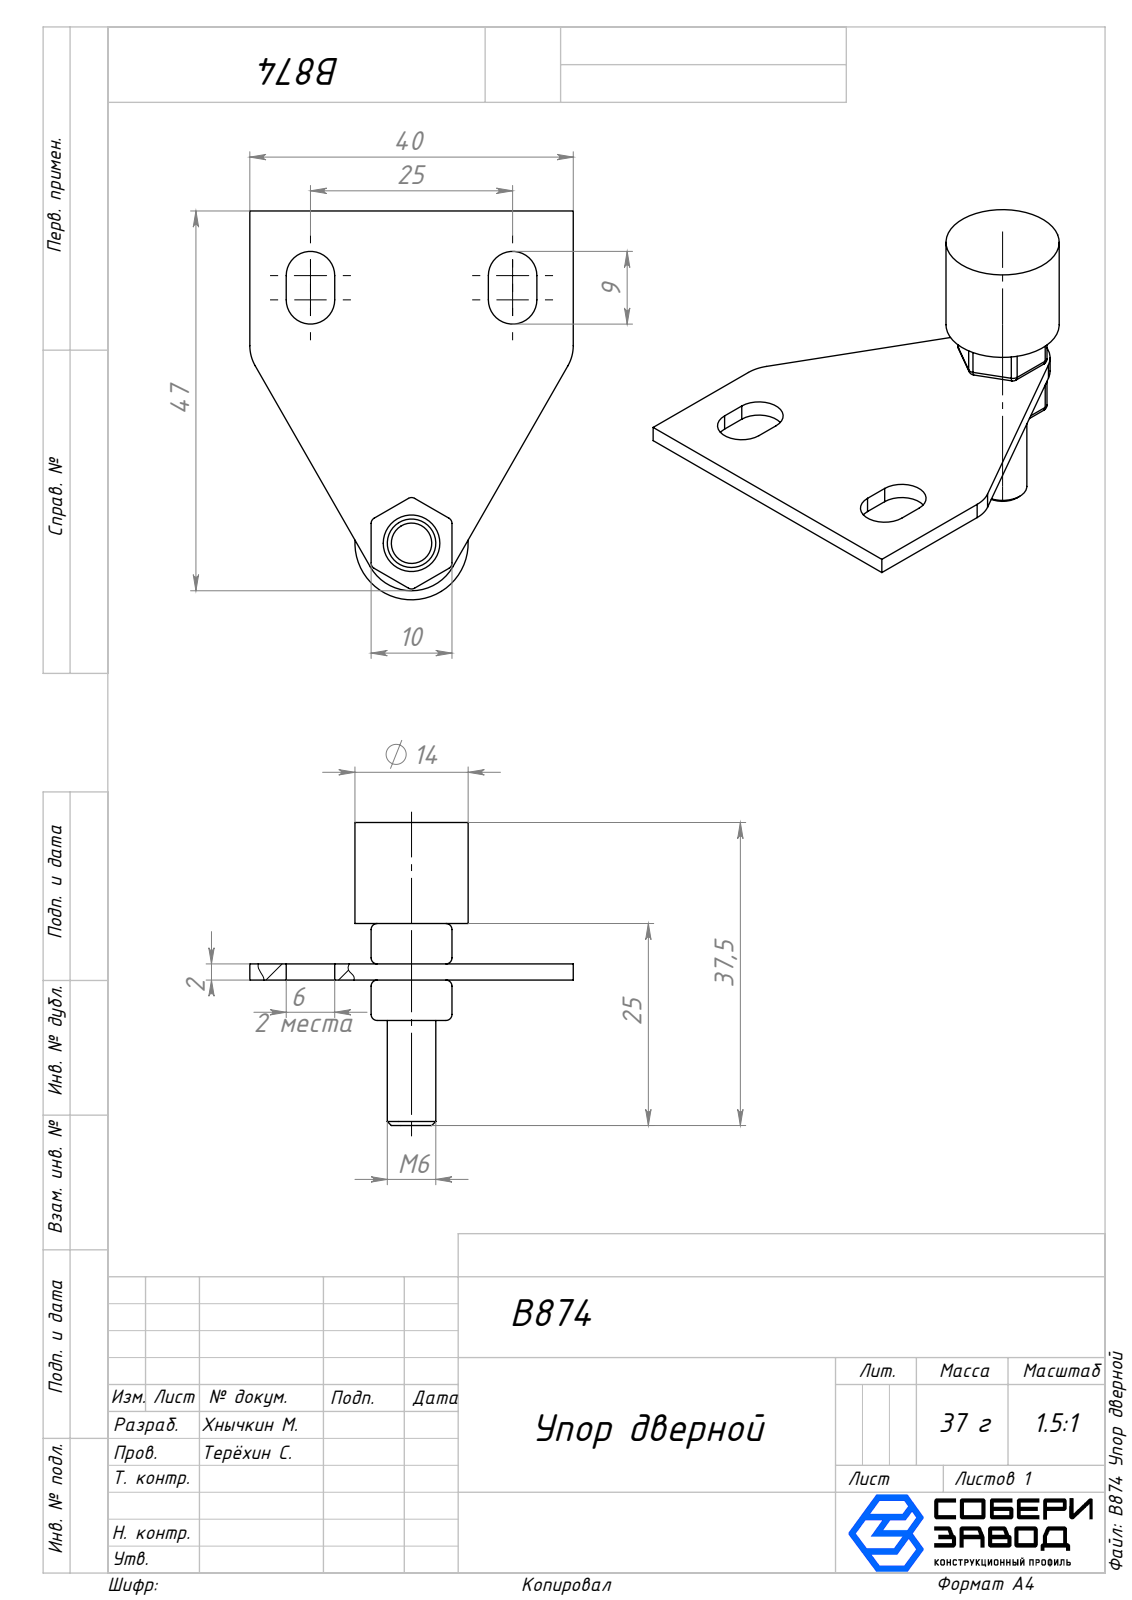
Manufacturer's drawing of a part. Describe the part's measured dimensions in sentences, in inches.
The part is named "Винт_00; B874 Упор дверной; Пластина_00; Гайка_00". Its 3-D file was written by "SolidWorks 2025 (AUTOMOTIVE_DESIGN)". It is 4 solids with 120 faces: 30 planar, 56 cylindrical and 34 other. Overall it measures 1.894 by 1.575 by 1.476 inches. Its volume is 0.354 cubic inches and its surface area 7.741 square inches. Round holes: 1 of diameter 0.197, 1 of diameter 0.236. Round bosses or shafts: 1 of diameter 0.551. Partial cylindrical surfaces (rounded edges, fillets, slot ends): 30 of radius 0.03, 4 of radius 0.118, 2 of radius 0.197, 1 of radius 0.231. The main face-to-face distances are 0.079, 0.197, 0.276, 0.768, 0.689, 0.492, 0.394, 0.984, 0.591, 1.575.
